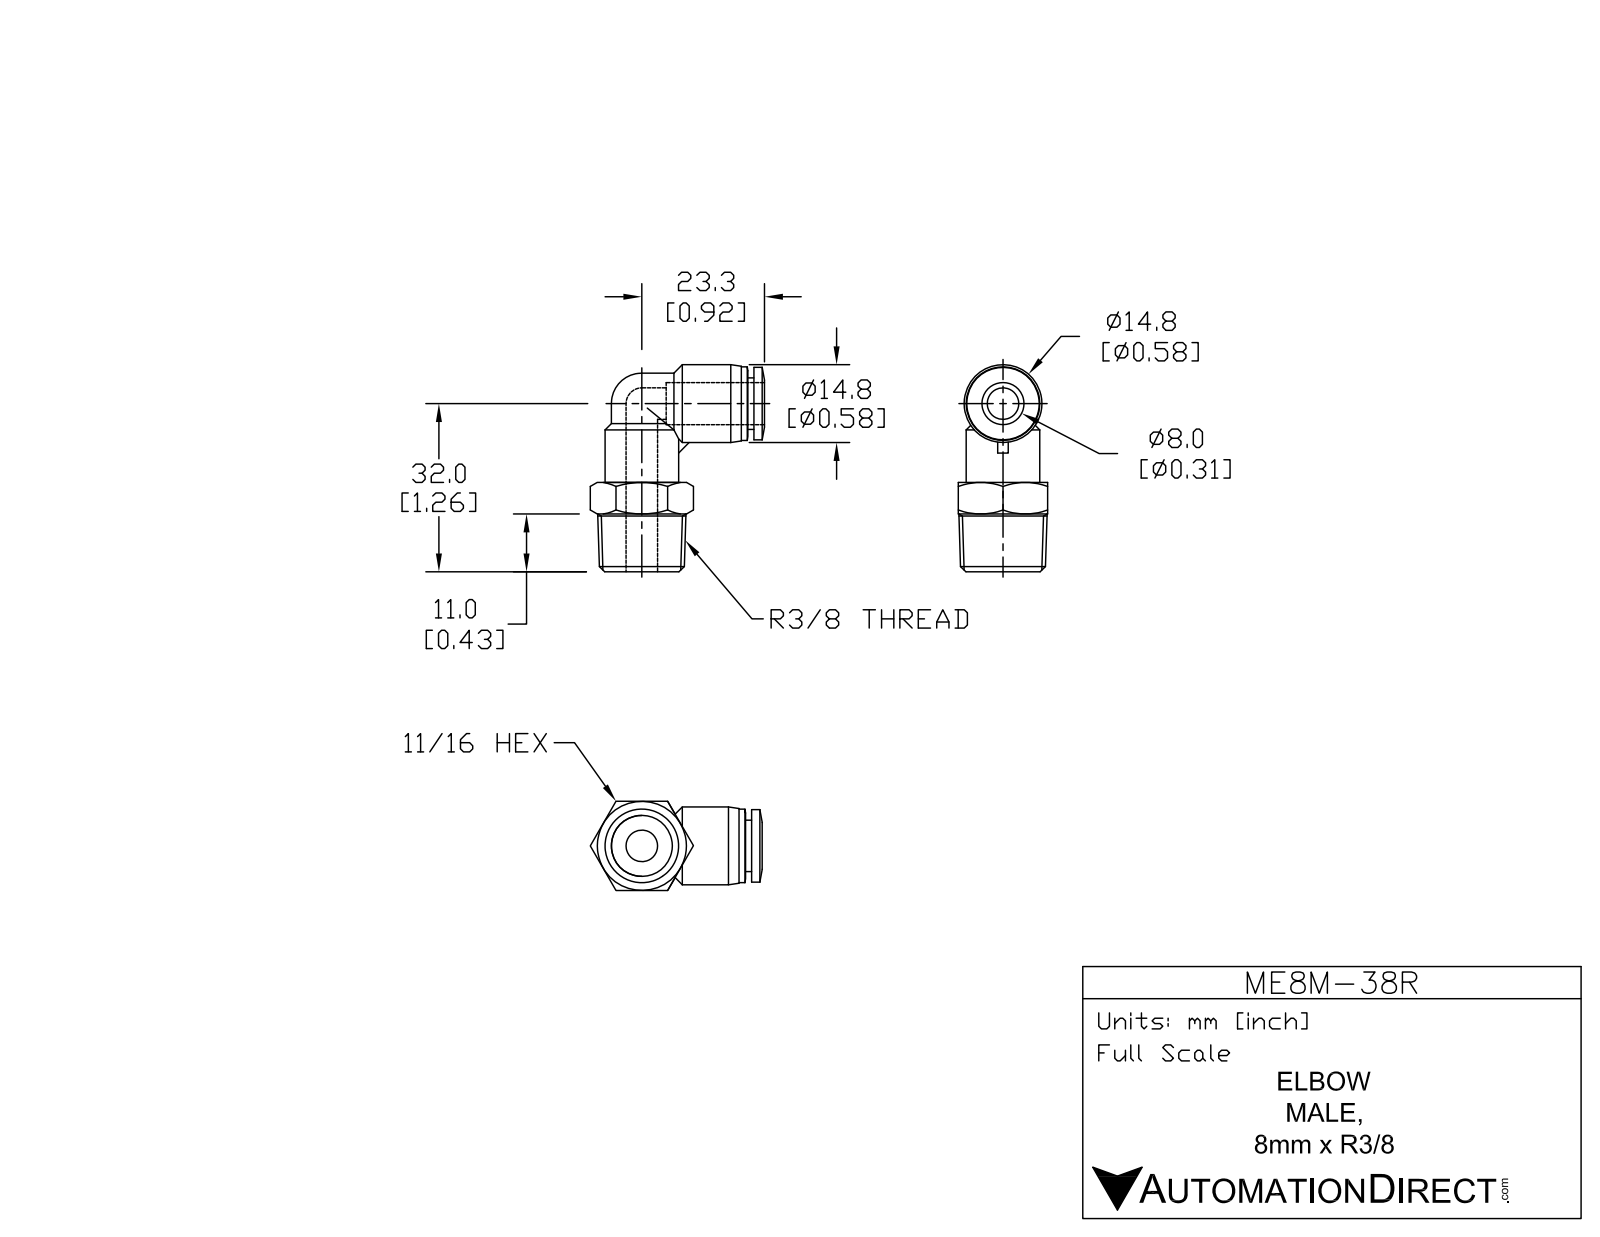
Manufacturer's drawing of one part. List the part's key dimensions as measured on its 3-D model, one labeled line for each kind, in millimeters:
Part name (STEP PRODUCT): ME8M-38R
STEP written by: SolidWorks 2015 (AUTOMOTIVE_DESIGN)
Units: millimetres
Bodies: 1 solid, 69 faces (17 planar, 19 cylindrical, 33 other)
Overall size (bounding box): 39.4 × 32.7 × 17
Volume: 7 100 mm³ · Surface area: 4 175 mm²
Round holes (diameter × count): ⌀6 ×2, ⌀8.3 ×1
Round bosses / shafts (diameter × count): ⌀14 ×2, ⌀14.8 ×1, ⌀13.8 ×1, ⌀11.6 ×1, ⌀9.8 ×1
Partial cylindrical surfaces — rounded edges, fillets, slot ends (radius × count): R5.8 ×1
Main face-to-face distances: 17, 1.1, 15.1, 16.3, 2, 18.3, 3.1, 11, 6, 7.5
